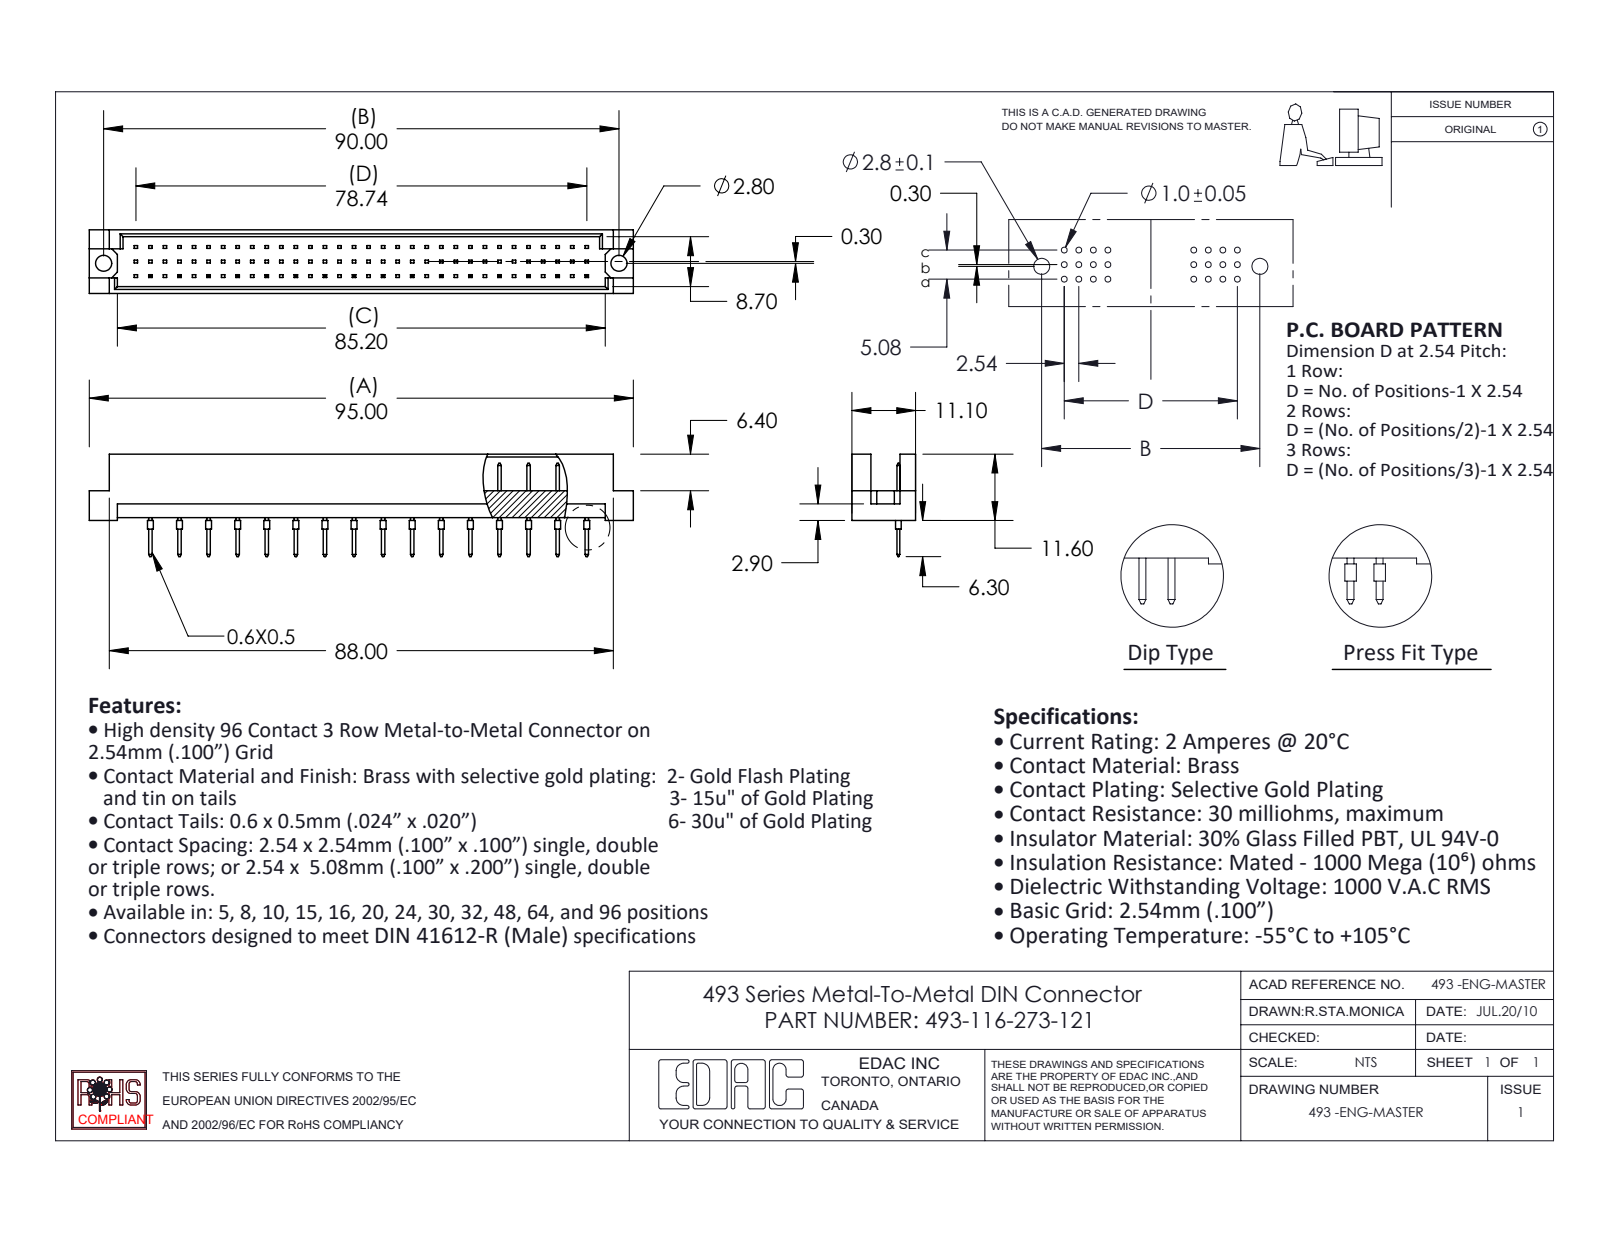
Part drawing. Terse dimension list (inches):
name: 493-116-273-122; 493-290_73; 493 Part_96
written by: SolidWorks 2020 (CONFIG_CONTROL_DESIGN)
unit: in
bodies: 17 solids, 788 faces (752 planar, 36 cylindrical, 0 other)
size: 3.74 × 0.705 × 0.437
volume: 0.351 in³; area: 10.97 in²
holes: 2× ⌀0.11
bosses: 16× ⌀0.039
face distances: 0.047, 0.39, 0.437, 0.343, 0.185, 0.02, 0.2, 0.1, 0.109, 0.128
hole spacings: 3.543
